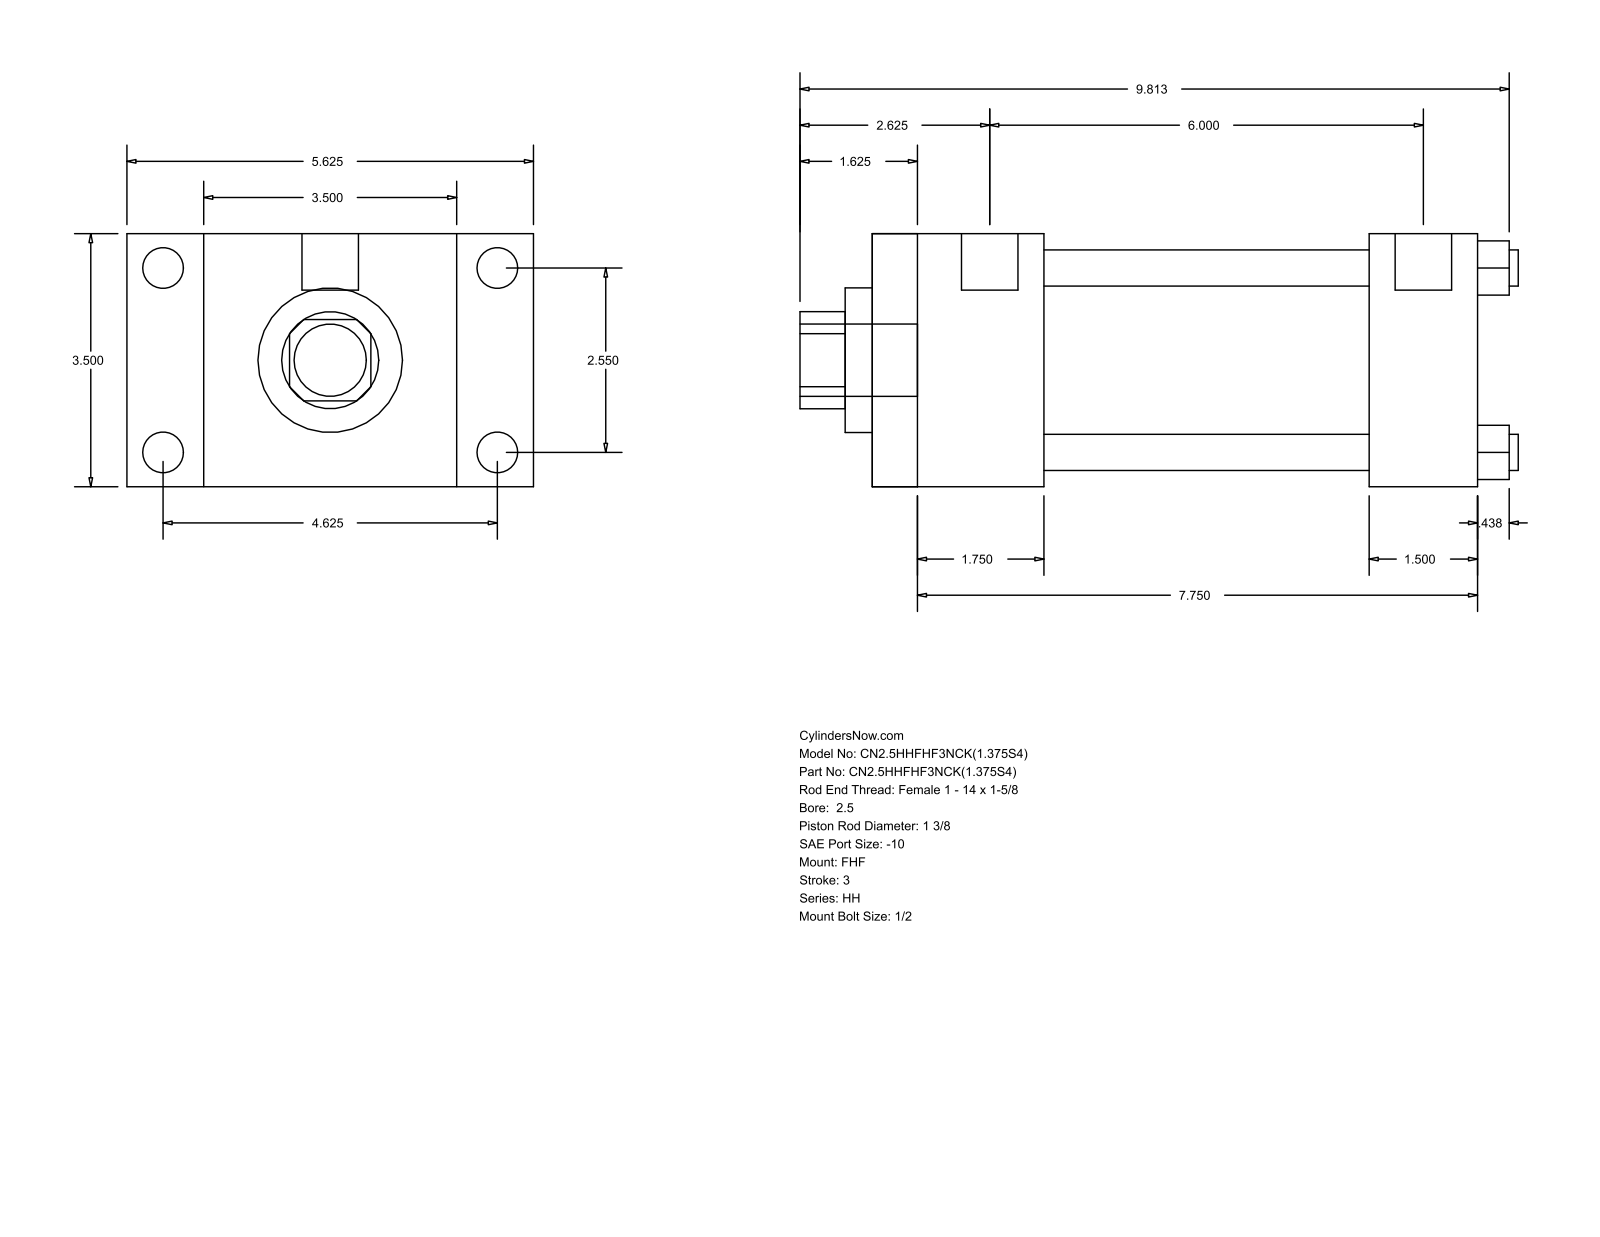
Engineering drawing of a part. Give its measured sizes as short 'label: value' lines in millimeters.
name: HH_FHF__0250_1.375
written by: GSSL Pune (CONFIG_CONTROL_DESIGN)
unit: mm
bodies: 0 solids, 88 faces (60 planar, 28 cylindrical, 0 other)
size: 252.41 × 142.88 × 88.9
holes: 4× ⌀12.7, 1× ⌀34.92, 1× ⌀50.8, 1× ⌀73.03
bosses: 4× ⌀14.3, 4× ⌀5.56, 2× ⌀19.84, 1× ⌀25.4
rounds: 1× R17.06
face distances: 88.9, 60.32, 26.99, 115.89, 212.72, 152.4, 142.88, 174.63, 114.31, 38.09
hole spacings: 45.79, 64.76, 91.58
